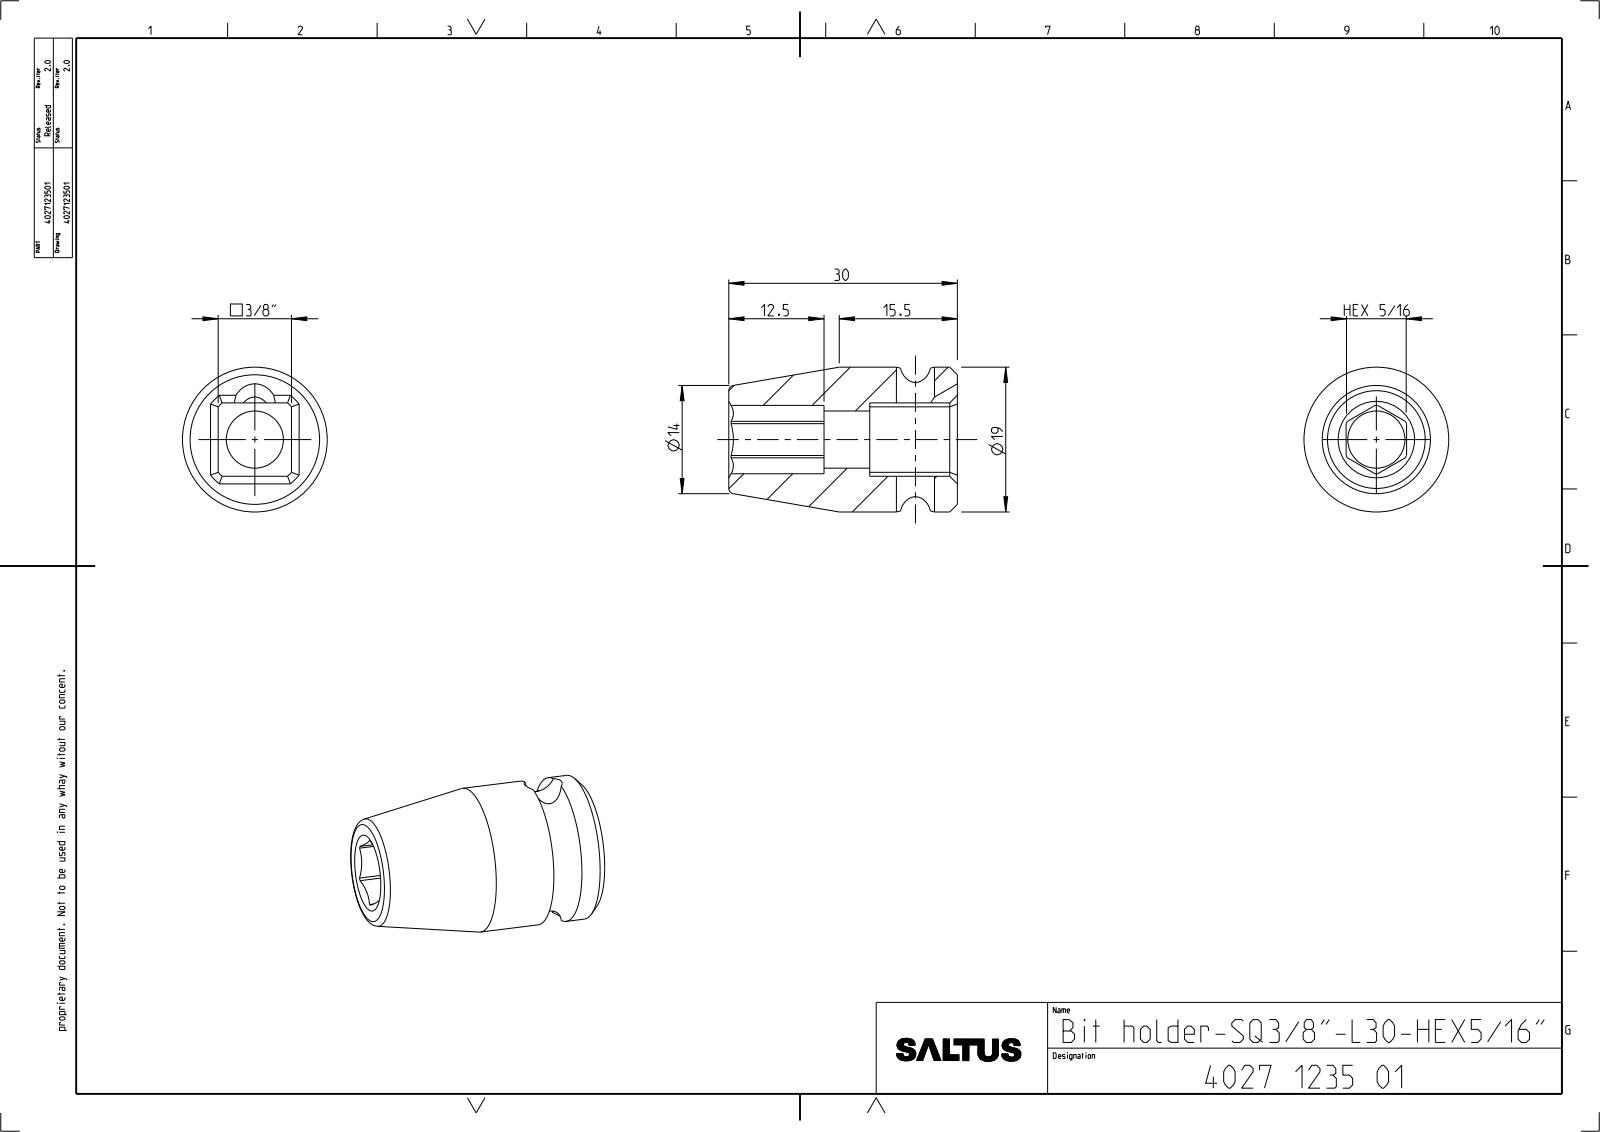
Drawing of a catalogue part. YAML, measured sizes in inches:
part_name: "4027123501"
step_written_by: "CREO PARAMETRIC BY PTC INC, 2022414 (CONFIG_CONTROL_DESIGN)"
units: inches
bodies: {solids: 1, faces: 54, planar: 19, cylindrical: 21, other: 14}
overall_size: [1.181, 0.748, 0.748]
volume: 0.308
surface_area: 4.582
round_holes:
  - {diameter: 0.197, count: 1}
  - {diameter: 0.295, count: 1}
round_bosses_or_shafts:
  - {diameter: 0.748, count: 1}
partial_cylinders:
  - {radius: 0.118, count: 1}
  - {radius: 0.177, count: 1}
  - {radius: 0.254, count: 1}
face_to_face_distances: [0.379, 0.313, 0.033, 0.346, 1.181, 0.453, 0.728, 0.689, 0.236, 0.492]
